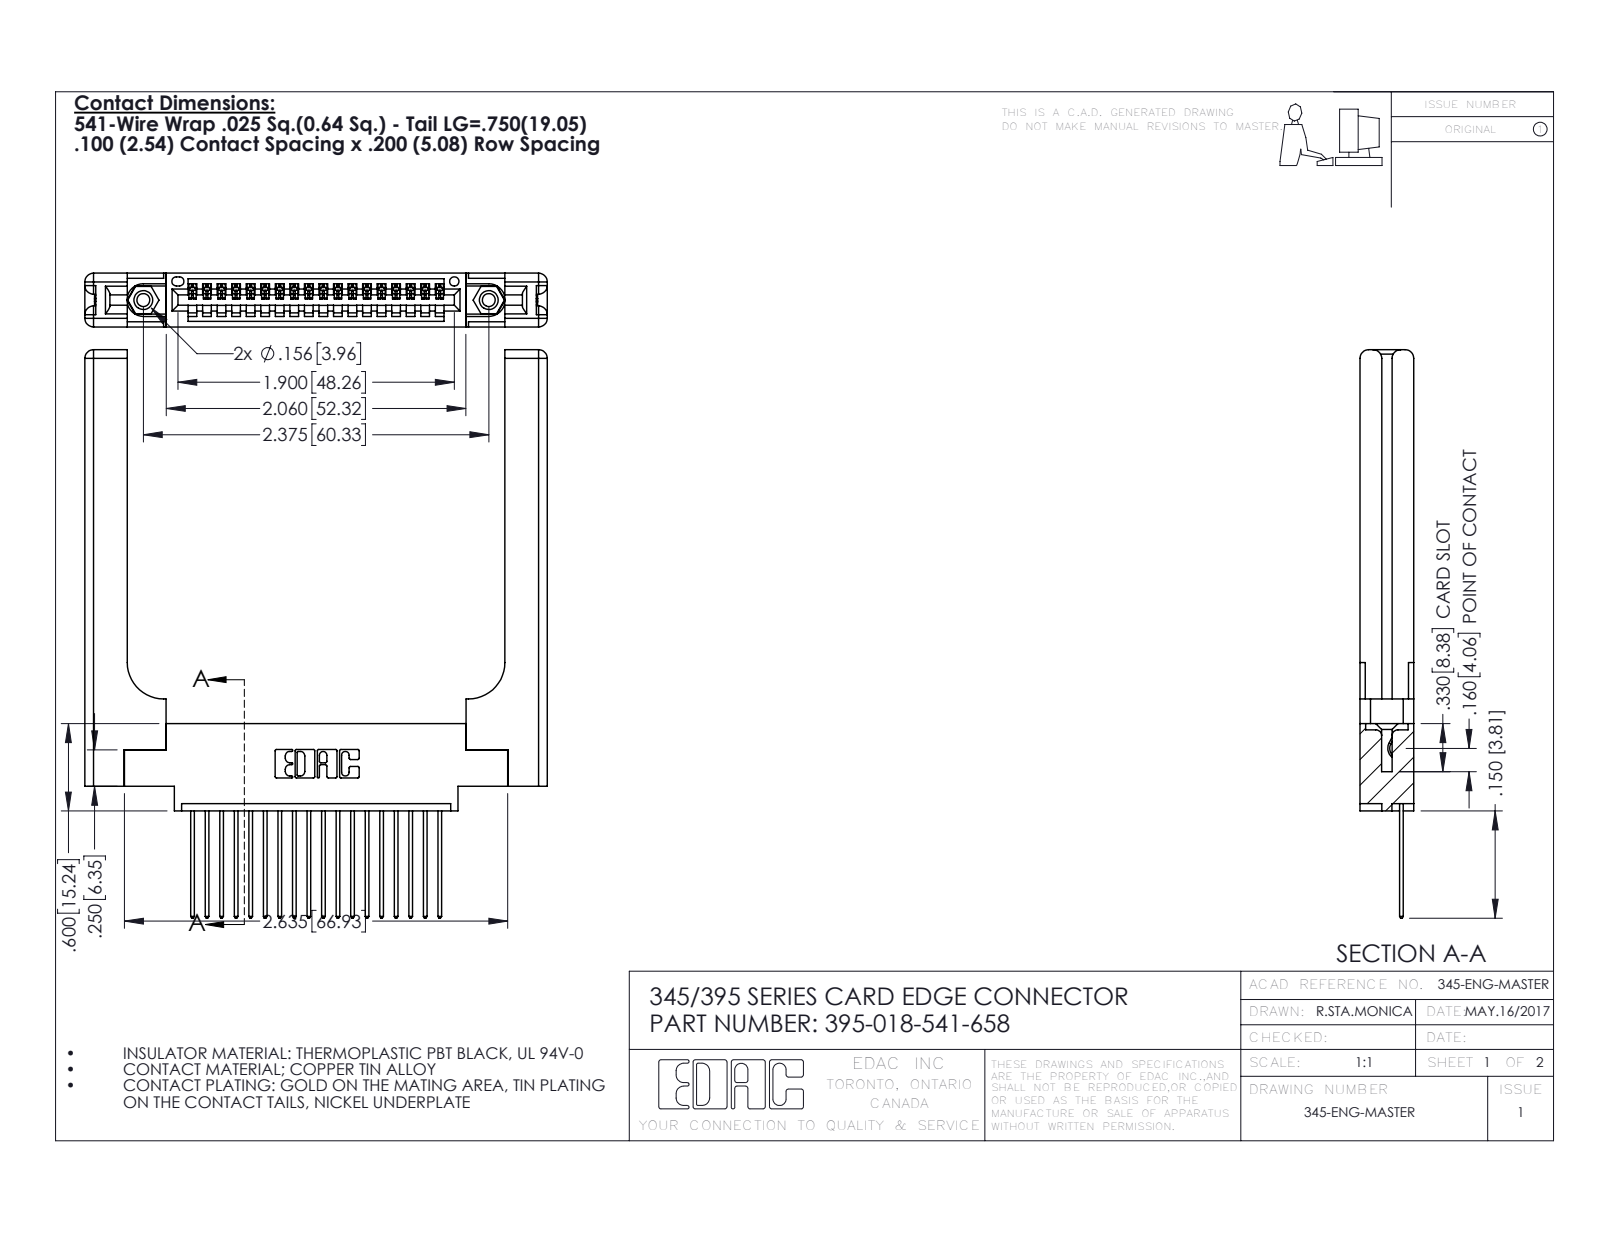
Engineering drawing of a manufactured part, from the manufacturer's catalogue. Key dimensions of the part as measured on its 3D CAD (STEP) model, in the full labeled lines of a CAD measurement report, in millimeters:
Part name (STEP PRODUCT): 345-292-001_345-293-141; 345-220-058_345-220-058; 395-018-541-658; 345 Part_0.170 Offset - 0.156 Dia-TH (+1 more)
STEP written by: SolidWorks 2016 (CONFIG_CONTROL_DESIGN)
Units: millimetres
Bodies: 23 solids, 1430 faces (952 planar, 418 cylindrical, 60 other)
Overall size (bounding box): 99.2 × 80.7 × 9.4
Volume: 15 900 mm³ · Surface area: 15 320 mm²
Round holes (diameter × count): ⌀2.3 ×2, ⌀3.2 ×2, ⌀4 ×2, ⌀1.6 ×1
Round bosses / shafts (diameter × count): ⌀3.9 ×2
Partial cylindrical surfaces — rounded edges, fillets, slot ends (radius × count): R0.2 ×36, R0.3 ×36, R0.3 ×22, R1.5 ×16, R0.2 ×6, R0.8 ×6, R0.7 ×3, R0.8 ×2
Main face-to-face distances: 9.4, 1.8, 7.6, 3.8, 3.8, 2, 5.6, 2.5, 6.9, 0.6
Hole centre spacings: 6.9, 54.4, 60.3
